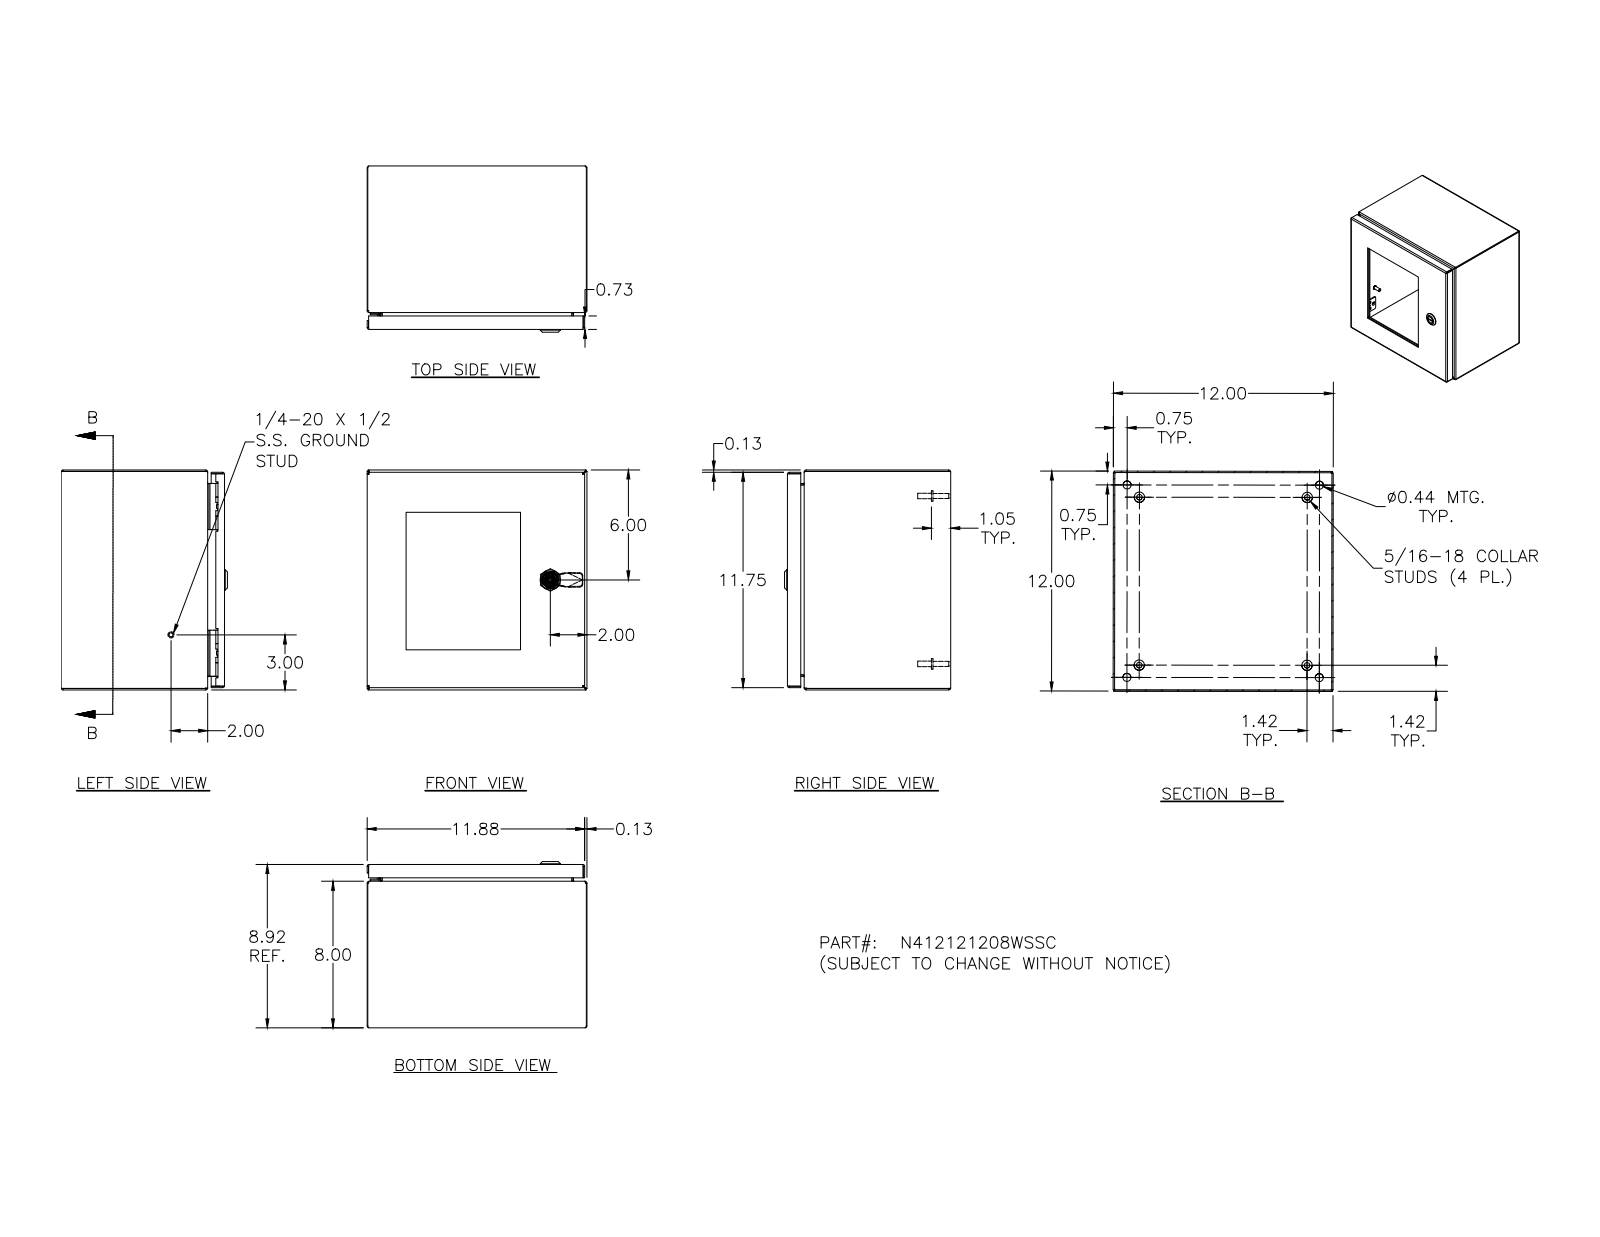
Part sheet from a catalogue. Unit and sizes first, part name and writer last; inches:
Units: inches
Overall size (bounding box): 12 × 12 × 9.075
Round holes (diameter × count): ⌀0.156 ×10, ⌀0.281 ×8, ⌀0.093 ×4, ⌀0.152 ×4, ⌀0.167 ×4, ⌀0.172 ×4, ⌀0.188 ×4, ⌀0.437 ×4, ⌀0.187 ×1, ⌀0.197 ×1, ⌀0.315 ×1, ⌀0.394 ×1
Round bosses / shafts (diameter × count): ⌀0.25 ×10, ⌀0.19 ×8, ⌀0.253 ×7, ⌀0.563 ×4, ⌀0.36 ×4, ⌀0.32 ×4, ⌀0.3 ×4, ⌀0.275 ×4
Partial cylindrical surfaces — rounded edges, fillets, slot ends (radius × count): R0.031 ×34, R0.05 ×26, R0.105 ×24, R0.016 ×18, R0.125 ×16, R0.02 ×9, R0.032 ×8, R0.157 ×4
Main face-to-face distances: 0.074, 11.926, 8.843, 11.852, 12, 8.769, 8.917, 0.25, 8.593, 8.519
Hole centre spacings: 8, 4, 6.221, 8.585, 10.5, 8.927, 0.5, 0.656
Volume: 72.23 in³ · Surface area: 1 690 in²
Bodies: 54 solids, 1684 faces (666 planar, 533 cylindrical, 485 other)
Part name (STEP PRODUCT): N412121208WSSC; N412121208WSSCBKP; N4121212WSSCLID; HFW328176 (+8 more)
STEP written by: Autodesk Inventor 2011 (AUTOMOTIVE_DESIGN)
